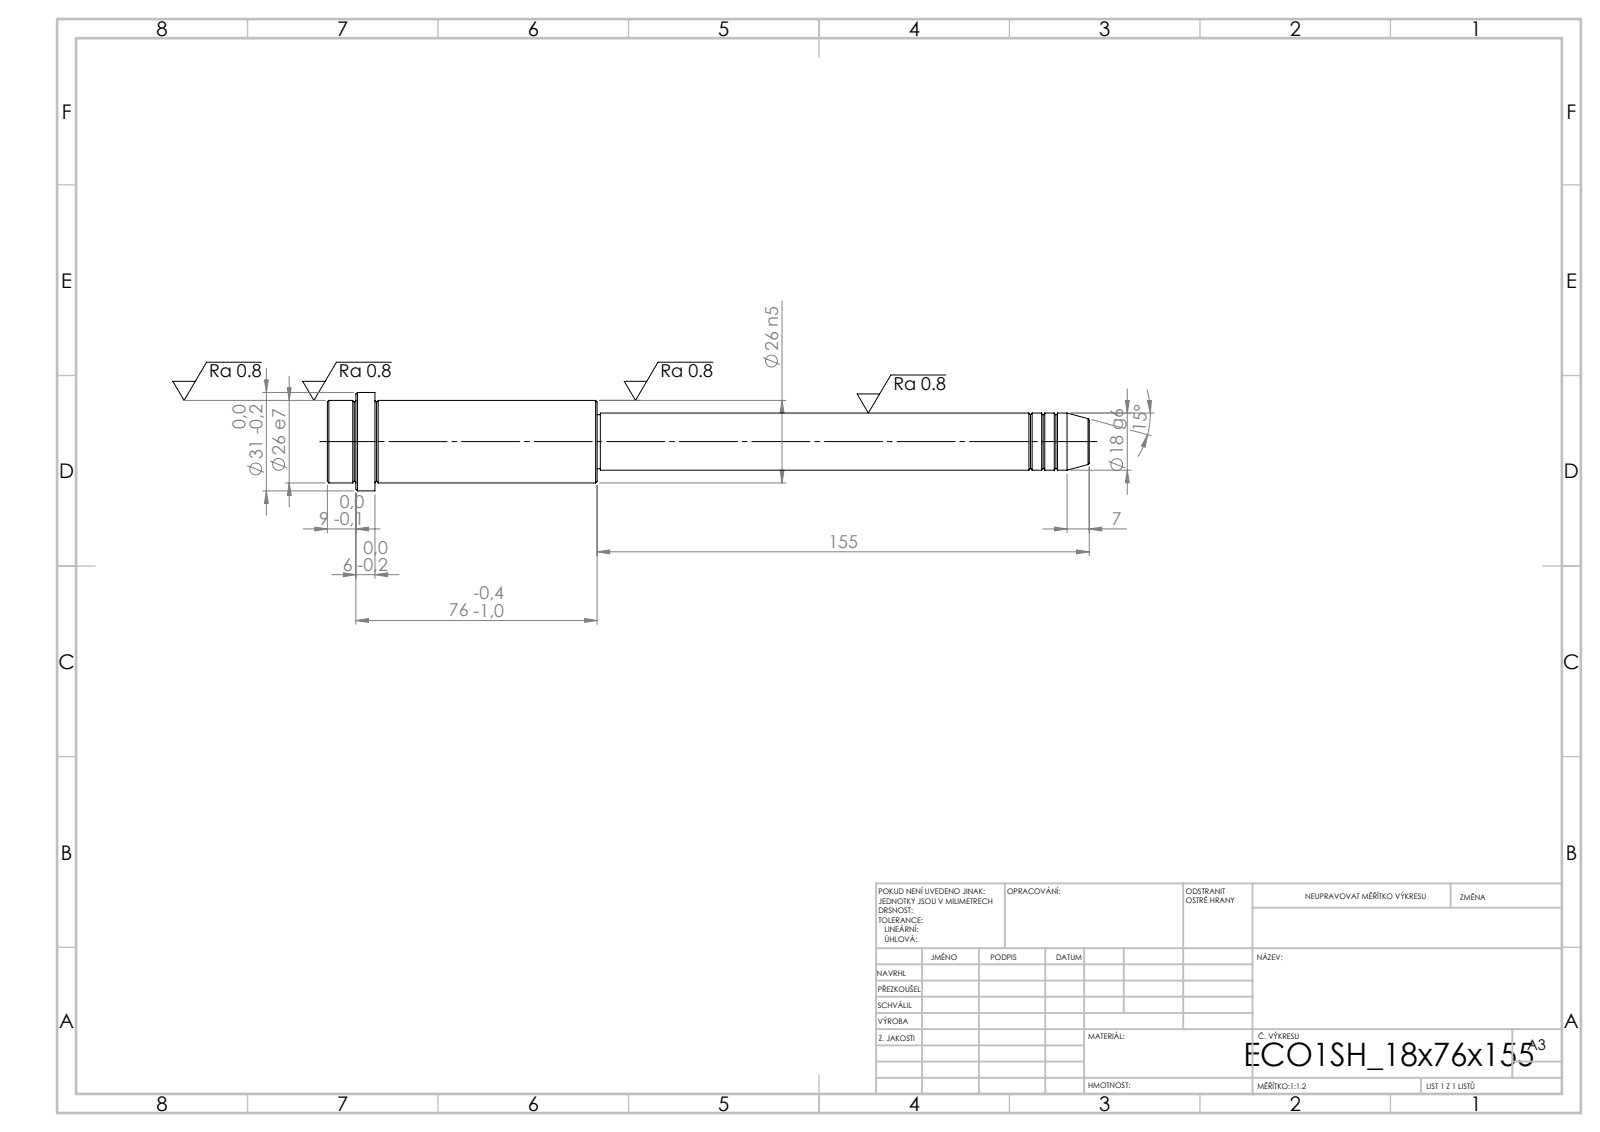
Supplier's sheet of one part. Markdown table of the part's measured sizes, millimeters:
| quantity | value |
| --- | --- |
| STEP written by | SolidWorks 2019 (CONFIG_CONTROL_DESIGN) |
| units | millimeters |
| bodies | 1 solid, 52 faces (6 planar, 16 cylindrical, 30 other) |
| overall size | 240 × 31 × 31 |
| volume | 85 380 mm³ |
| surface area | 17 332 mm² |
| round bosses / shafts (diameter × count) | 31 × 1, 26 × 1, 18 × 1, 17 × 1 |
| main face-to-face distances | 85, 70, 15, 76, 6, 9, 155, 225, 231, 240 |
